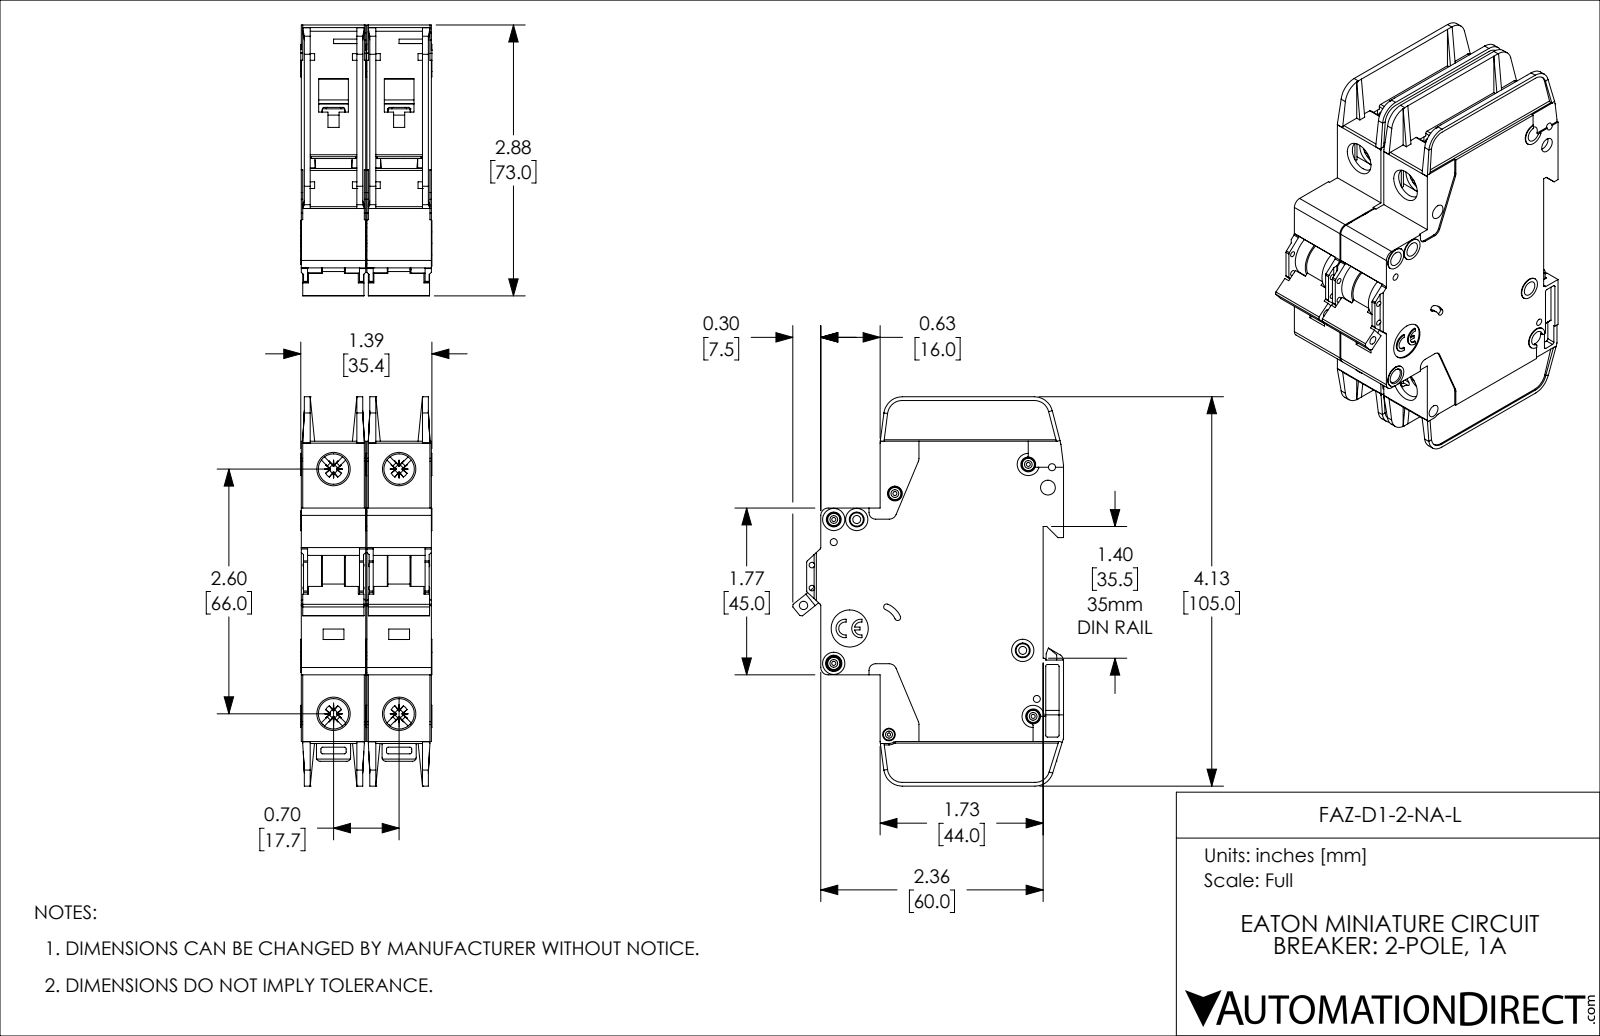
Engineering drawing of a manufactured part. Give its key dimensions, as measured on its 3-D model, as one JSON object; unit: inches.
{"part_name": "FAZ-D1-2-NA-L", "step_written_by": "SolidWorks 2019 (AUTOMOTIVE_DESIGN)", "units": "inches", "bodies": {"solids": 2, "faces": 2254, "planar": 1342, "cylindrical": 714, "other": 198}, "overall_size": [4.134, 2.876, 1.394], "volume_in3": 9.365, "surface_area_in2": 82.01, "round_holes": [[0.157, 8], [0.043, 5], [0.075, 4], [0.323, 4], [0.059, 2], [0.085, 2], [0.035, 1], [0.089, 1], [0.098, 1], [0.134, 1], [0.394, 1]], "round_bosses_or_shafts": [[0.13, 5], [0.236, 4], [0.118, 3], [0.098, 2]], "partial_cylinders_radius": [[0.02, 57], [0.016, 20], [0.039, 14], [0.079, 10], [0.043, 8], [0.008, 5], [0.197, 5], [0.01, 4]], "face_to_face_distances": [0.697, 0.047, 0.685, 0.591, 0.094, 0.638, 0.543, 1.382, 0.744, 0.65], "hole_center_spacings": [0.244, 0.537, 0.697, 0.87, 2.598, 2.69, 0.189, 0.199]}
